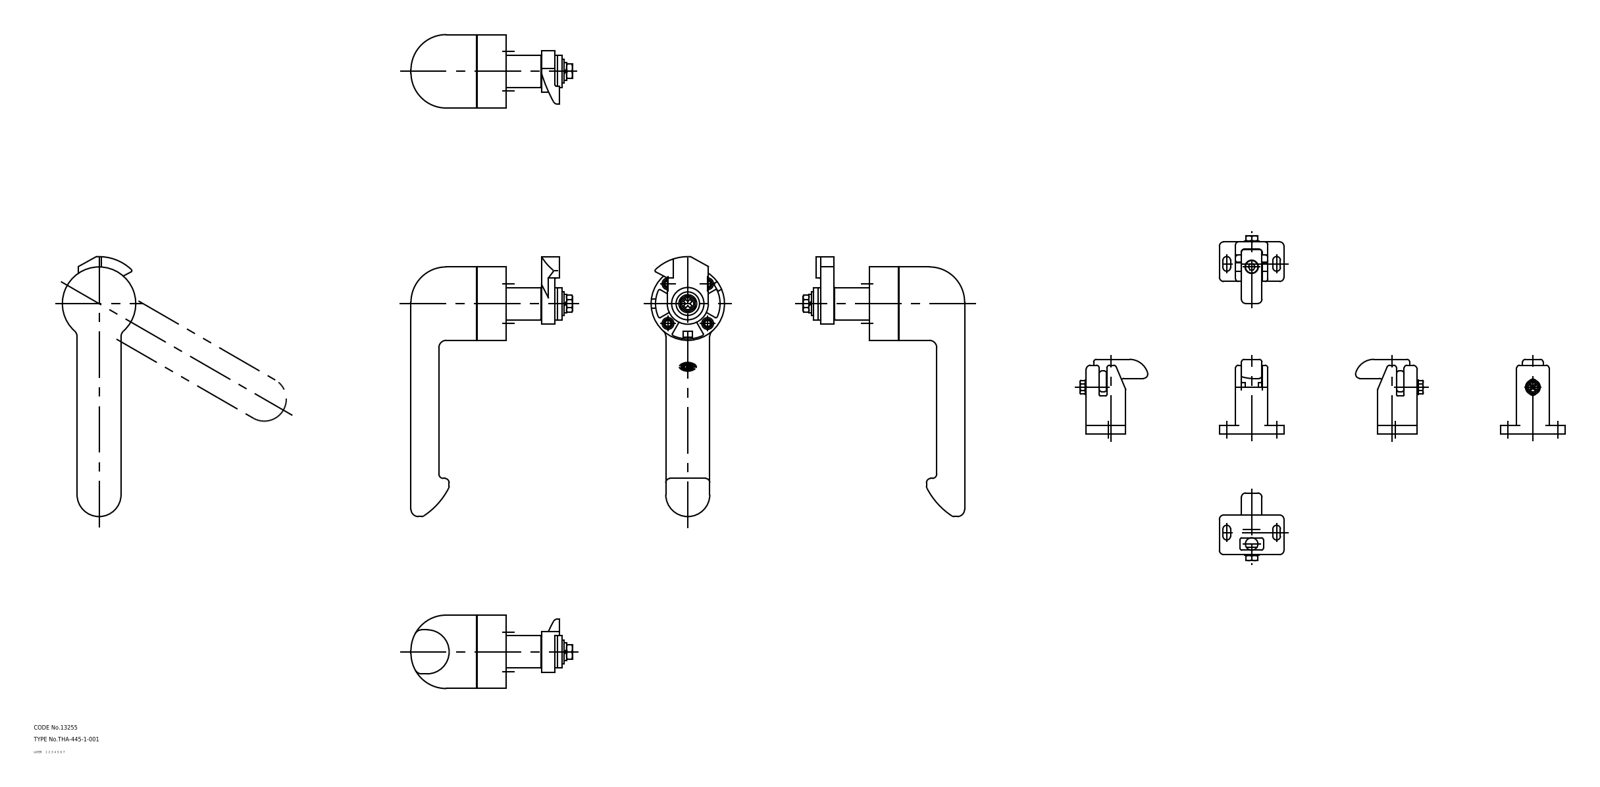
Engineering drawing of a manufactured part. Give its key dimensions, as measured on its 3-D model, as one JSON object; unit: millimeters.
{"part_name": "67134905; 67134918; 67134931; 67134944 (+5 more)", "step_written_by": "CADfix (AUTOMOTIVE_DESIGN)", "units": "millimeters", "bodies": {"solids": 9, "faces": 500, "planar": 0, "cylindrical": 0, "other": 500}, "overall_size": [210.1, 127, 53.25], "volume_mm3": 217692, "surface_area_mm2": 58038}
